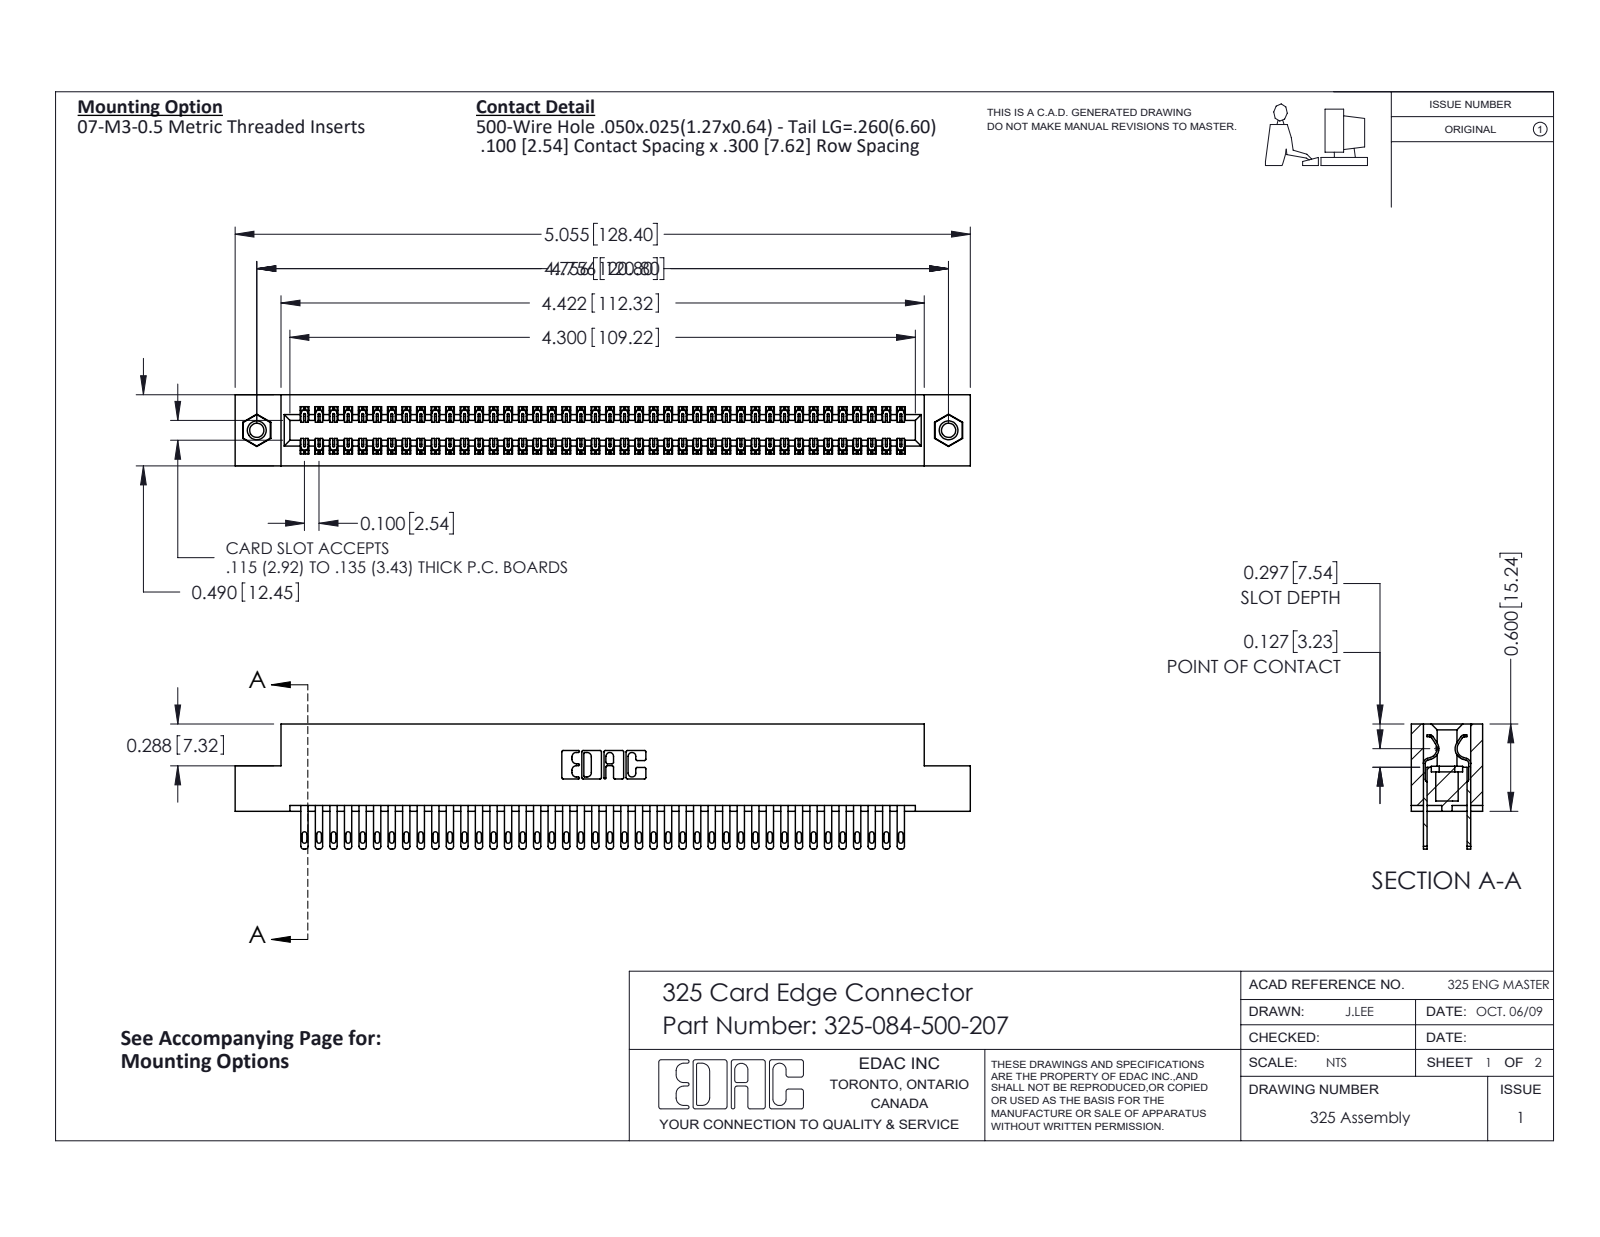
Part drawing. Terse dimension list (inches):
name: 325-292-001_325-293-100; 345-250-001_345-250-005-103; 325-084-500-207; 325 Part_TI
written by: SolidWorks 2016 (CONFIG_CONTROL_DESIGN)
unit: in
bodies: 87 solids, 4206 faces (2622 planar, 1568 cylindrical, 16 other)
size: 5.055 × 0.86 × 0.49
volume: 1.026 in³; area: 32.96 in²
holes: 2× ⌀0.098, 2× ⌀0.125, 2× ⌀0.16
bosses: 2× ⌀0.155
rounds: 126× R0.006, 84× R0.016, 84× R0.02, 22× R0.01, 6× R0.007, 6× R0.031, 3× R0.026, 2× R0.014
face distances: 0.083, 0.407, 0.3, 0.107, 0.383, 0.025, 0.49, 0.325, 0.275, 0.56
hole spacings: 4.756
